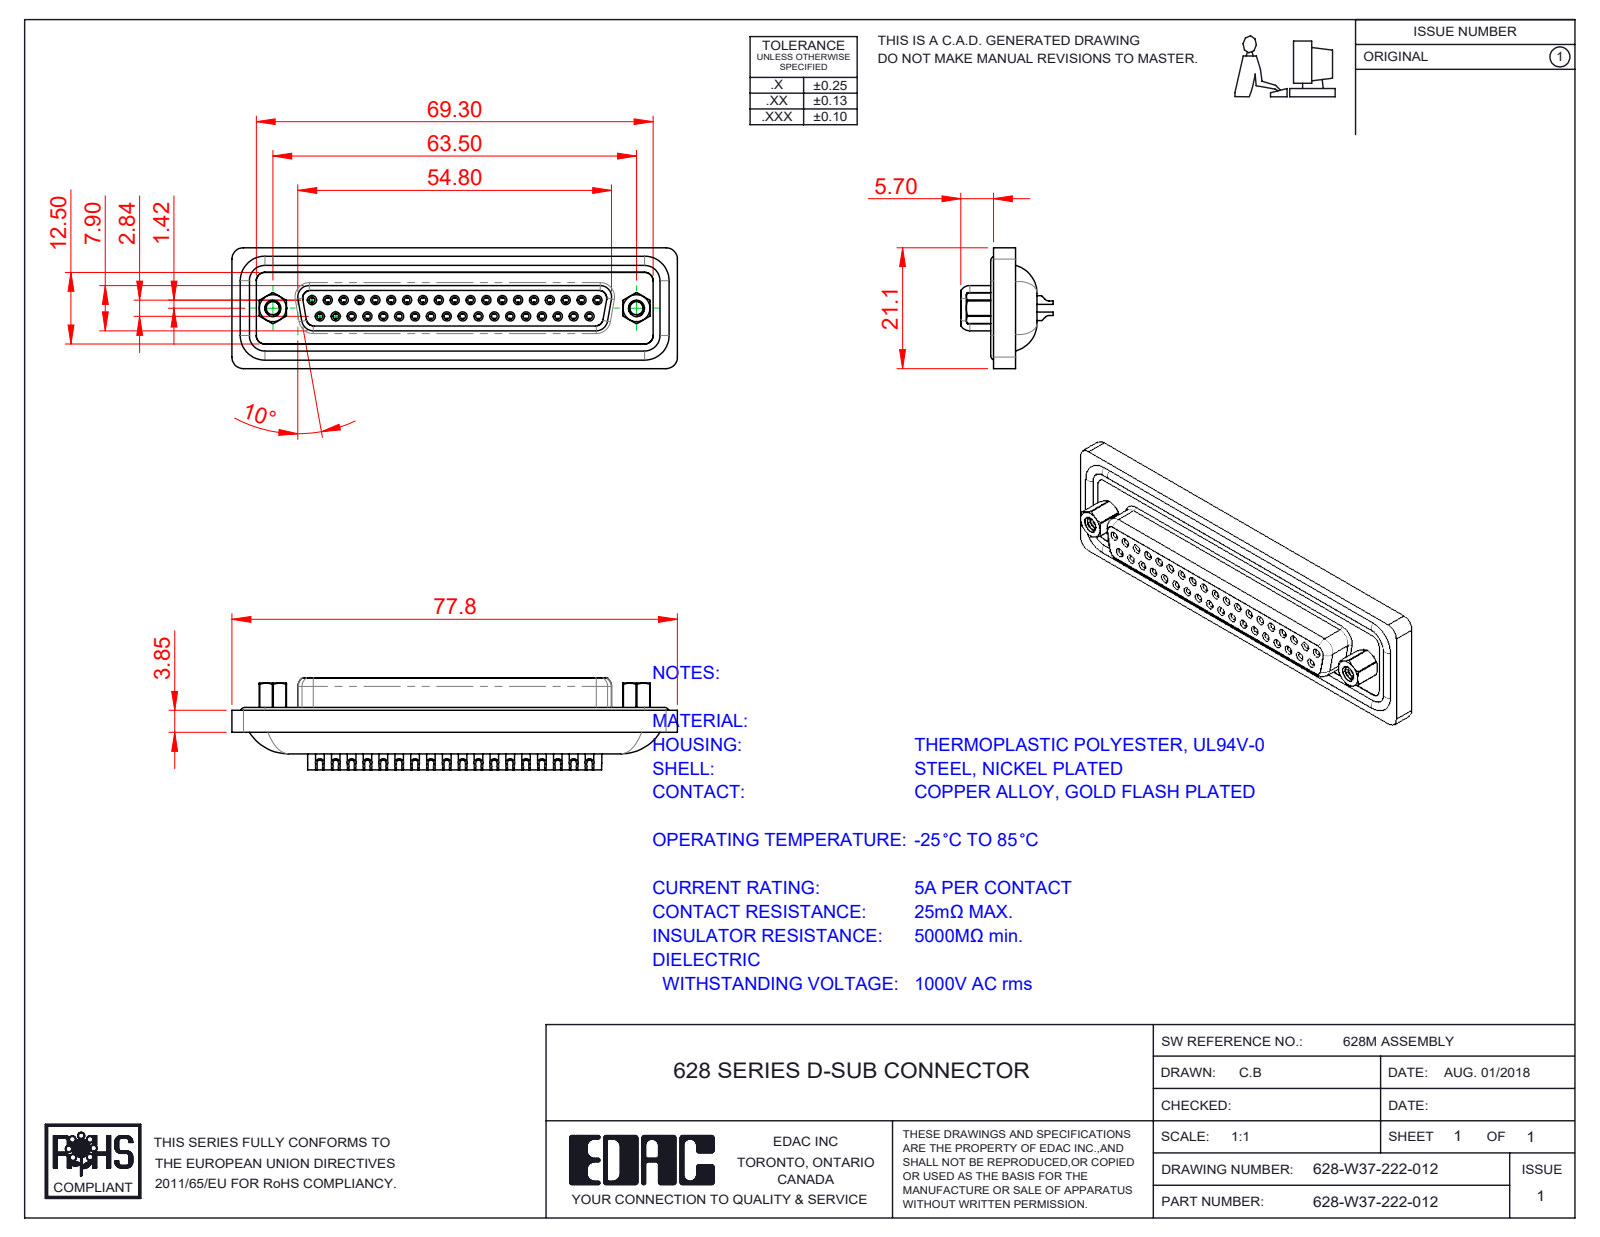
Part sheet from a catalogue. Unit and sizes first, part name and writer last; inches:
Units: inches
Overall size (bounding box): 3.063 × 0.831 × 0.634
Round holes (diameter × count): ⌀0.039 ×37, ⌀0.043 ×37, ⌀0.059 ×37, ⌀0.067 ×37, ⌀0.071 ×37, ⌀0.079 ×37, ⌀0.089 ×2, ⌀0.09 ×2, ⌀0.157 ×2, ⌀0.189 ×2, ⌀0.197 ×2
Round bosses / shafts (diameter × count): ⌀0.063 ×41, ⌀0.087 ×37, ⌀0.059 ×8, ⌀0.193 ×2, ⌀0.11 ×2
Partial cylindrical surfaces — rounded edges, fillets, slot ends (radius × count): R0.079 ×16, R0.059 ×14, R0.053 ×8, R0.106 ×6, R0.02 ×4, R0.035 ×4, R0.063 ×4, R0.069 ×4
Main face-to-face distances: 0.016, 0.293, 0.295, 0.333, 0.244, 0.537, 0.161, 0.043, 0.108, 0.315
Hole centre spacings: 0.124, 0.109, 0.218, 0.327, 0.198, 0.295, 0.436, 0.545
Volume: 0.676 in³ · Surface area: 28.04 in²
Bodies: 45 solids, 2532 faces (730 planar, 1071 cylindrical, 731 other)
Part name (STEP PRODUCT): 628W Shell Front_37 Contacts; 628-W37-222-012; 628W 4-40 Hex Standoff; 628W Contact Row 2_22 (+4 more)
STEP written by: SolidWorks 2020 (CONFIG_CONTROL_DESIGN)
